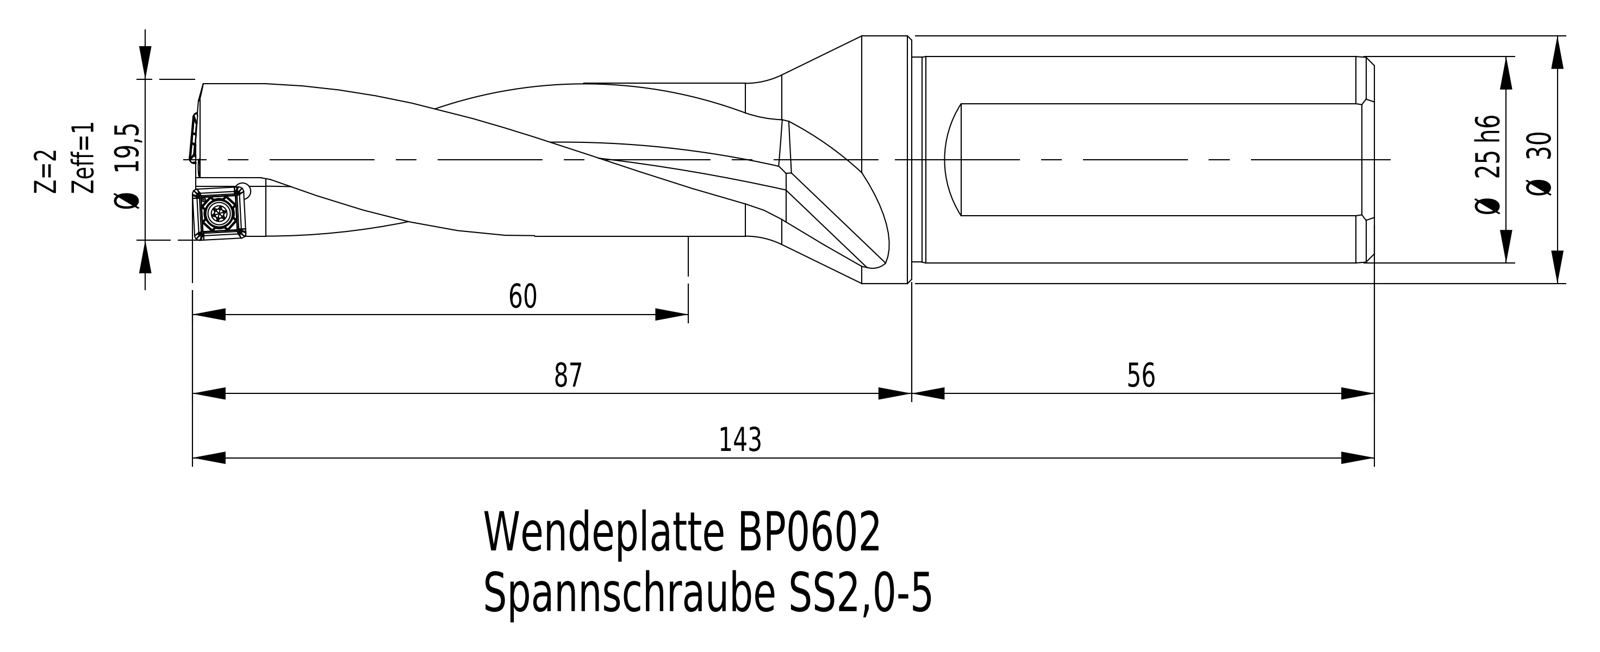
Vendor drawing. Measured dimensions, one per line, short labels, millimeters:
name: BW-19,5-60-25-06
written by: SolidWorks 2015 (AUTOMOTIVE_DESIGN)
unit: mm
bodies: 1 solid, 45 faces (7 planar, 14 cylindrical, 24 other)
size: 142.6 × 30 × 30
volume: 52 719 mm³; area: 12 344 mm²
holes: 1× ⌀4, 1× ⌀6.5
bosses: 1× ⌀30, 1× ⌀25, 1× ⌀24.8, 1× ⌀19.5, 1× ⌀18.5
face distances: 142.6, 86.6, 56, 5, 81.6, 137.6, 34.29
